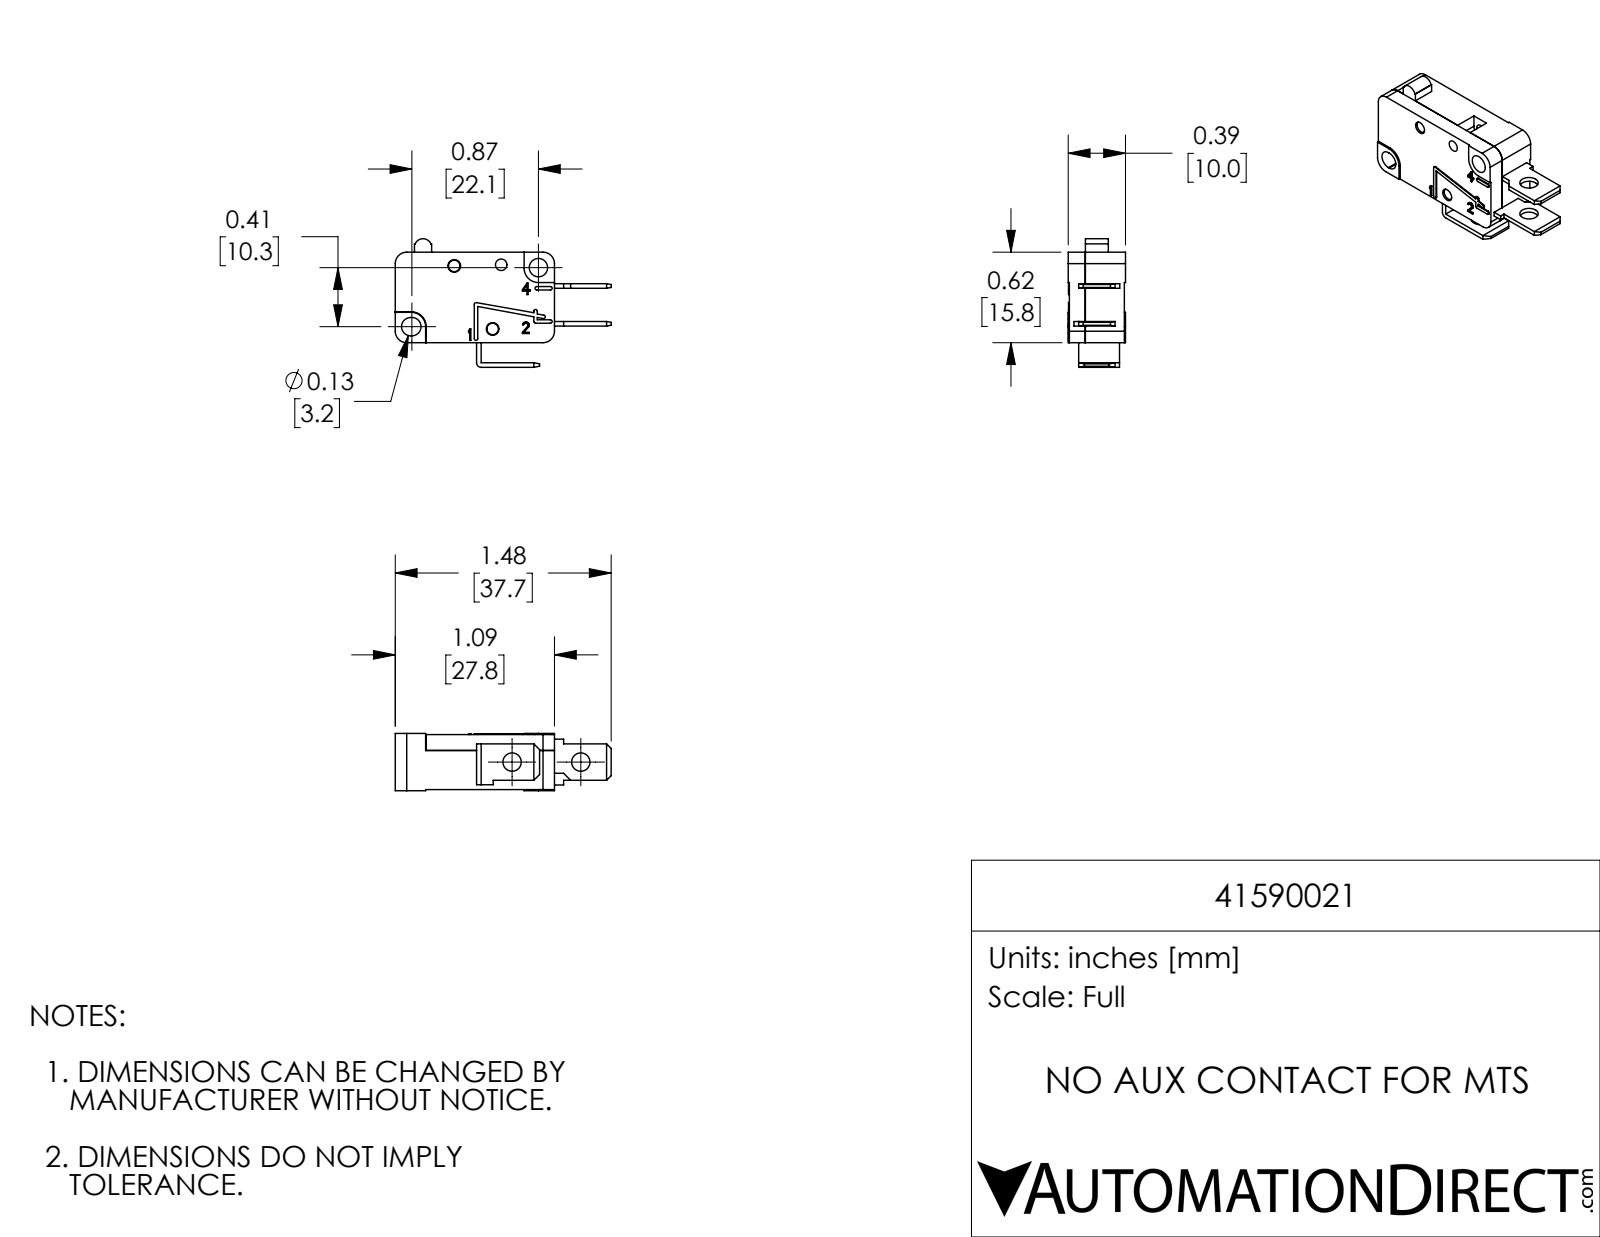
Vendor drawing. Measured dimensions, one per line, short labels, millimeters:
name: 41590021
written by: SolidWorks 2017 (AUTOMOTIVE_DESIGN)
unit: mm
bodies: 3 solids, 215 faces (153 planar, 60 cylindrical, 2 other)
size: 37.7 × 22.5 × 10
volume: 4 130 mm³; area: 3 332 mm²
holes: 3× ⌀3.2, 2× ⌀2.2, 1× ⌀2
bosses: 2× ⌀2
rounds: 9× R0.3, 4× R2, 2× R1.6, 2× R2.5, 1× R0.8, 1× R1.5, 1× R1.7, 1× R2.6
face distances: 6.8, 6.9, 9.6, 2.8, 2.7, 15.8, 0.8, 27.8, 6.6, 13.8
hole spacings: 6.5, 8.2, 11.3, 12, 12.9, 13.4, 14.7
